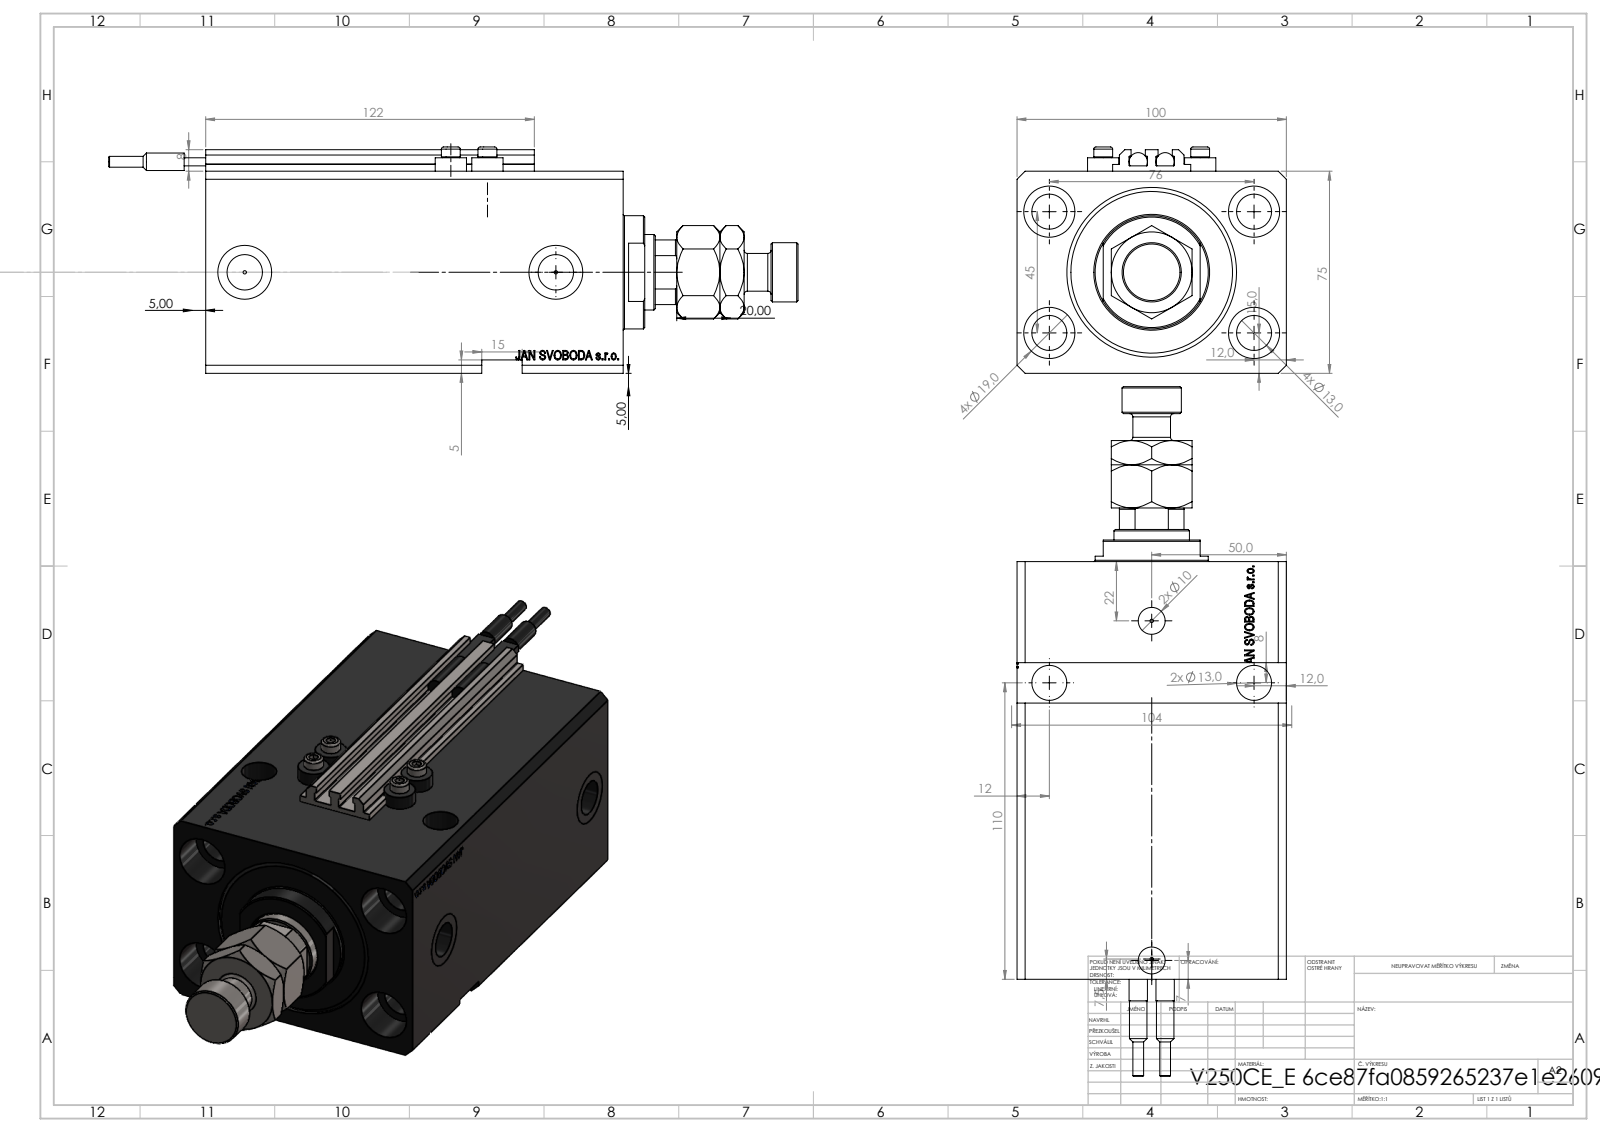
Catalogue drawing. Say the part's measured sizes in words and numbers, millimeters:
The part is named "V250CE_C_VCP; V250CE_E; MFA; V250CE_VC_E (+2 more)". Its 3-D file was written by "SolidWorks 2019 (CONFIG_CONTROL_DESIGN)". It is 11 solids with 1208 faces: 587 planar, 154 cylindrical and 467 other. Overall it measures 255.9 by 100 by 84 millimeters. Its volume is 979 290 cubic millimeters and its surface area 184 154 square millimeters. Round holes: 6 of diameter 13, 4 of diameter 1.25, 4 of diameter 4, 4 of diameter 19, 2 of diameter 10, 2 of diameter 13.16, 2 of diameter 20, 1 of diameter 18.5, 1 of diameter 28, 1 of diameter 50, 1 of diameter 63. Round bosses or shafts: 4 of diameter 11.6, 4 of diameter 7, 2 of diameter 6.8, 2 of diameter 6.5, 2 of diameter 4, 1 of diameter 42, 1 of diameter 22, 1 of diameter 14. Partial cylindrical surfaces (rounded edges, fillets, slot ends): 10 of radius 0.2, 1 of radius 13.5. The main face-to-face distances are 75, 100, 155, 11.9, 143.1, 128.4, 116.5, 26.6, 3, 48.4. The hole center spacings are 44.16, 76, 13.6, 20.72, 27.59, 33.62, 36, 38.48.
